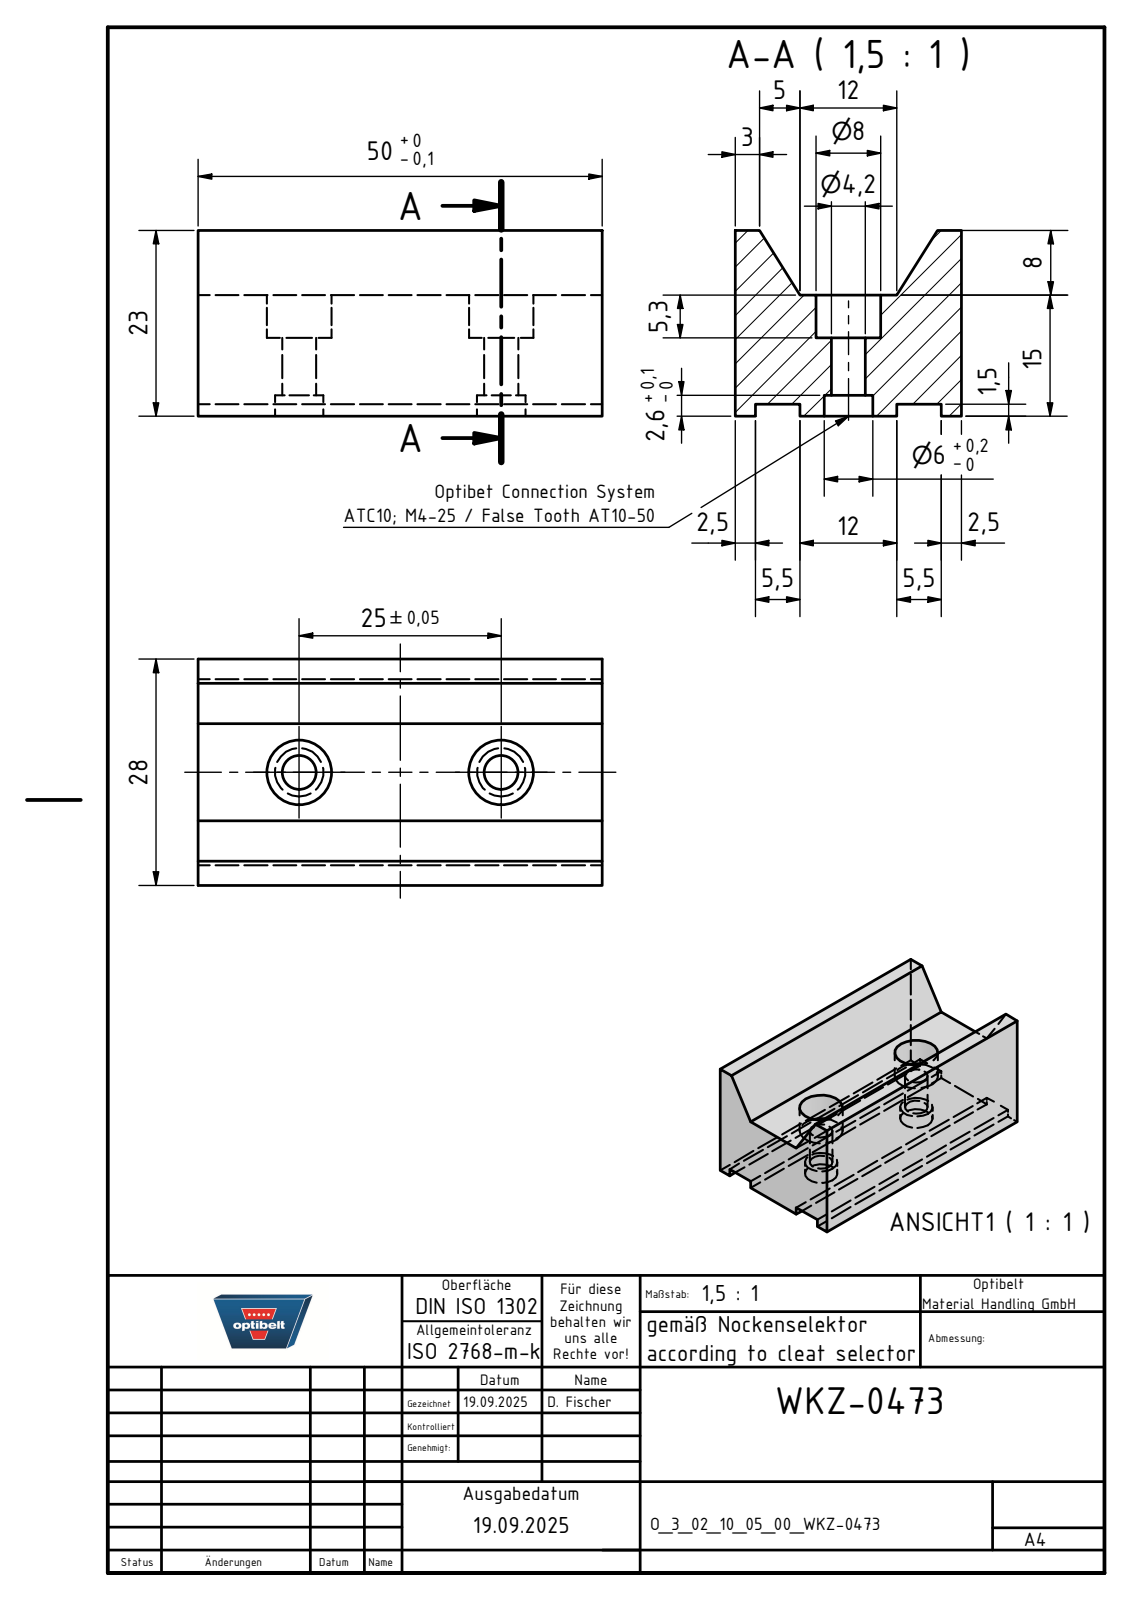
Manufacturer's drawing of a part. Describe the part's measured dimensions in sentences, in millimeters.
The part is named "O_3_02_10_05_00_WKZ-0473". Its 3-D file was written by "Autodesk Inventor 2025 (AUTOMOTIVE_DESIGN)". It is 1 solid with 28 faces: 22 planar, 6 cylindrical and 0 other. Overall it measures 50 by 28 by 23 millimeters. Its volume is 23 698 cubic millimeters and its surface area 7 323 square millimeters. Round holes: 2 of diameter 4.2, 2 of diameter 6, 2 of diameter 8. The main face-to-face distances are 28, 1.5, 15, 13.5, 50, 8, 23, 21.5, 2.5, 25.5. The hole center spacings are 25.
